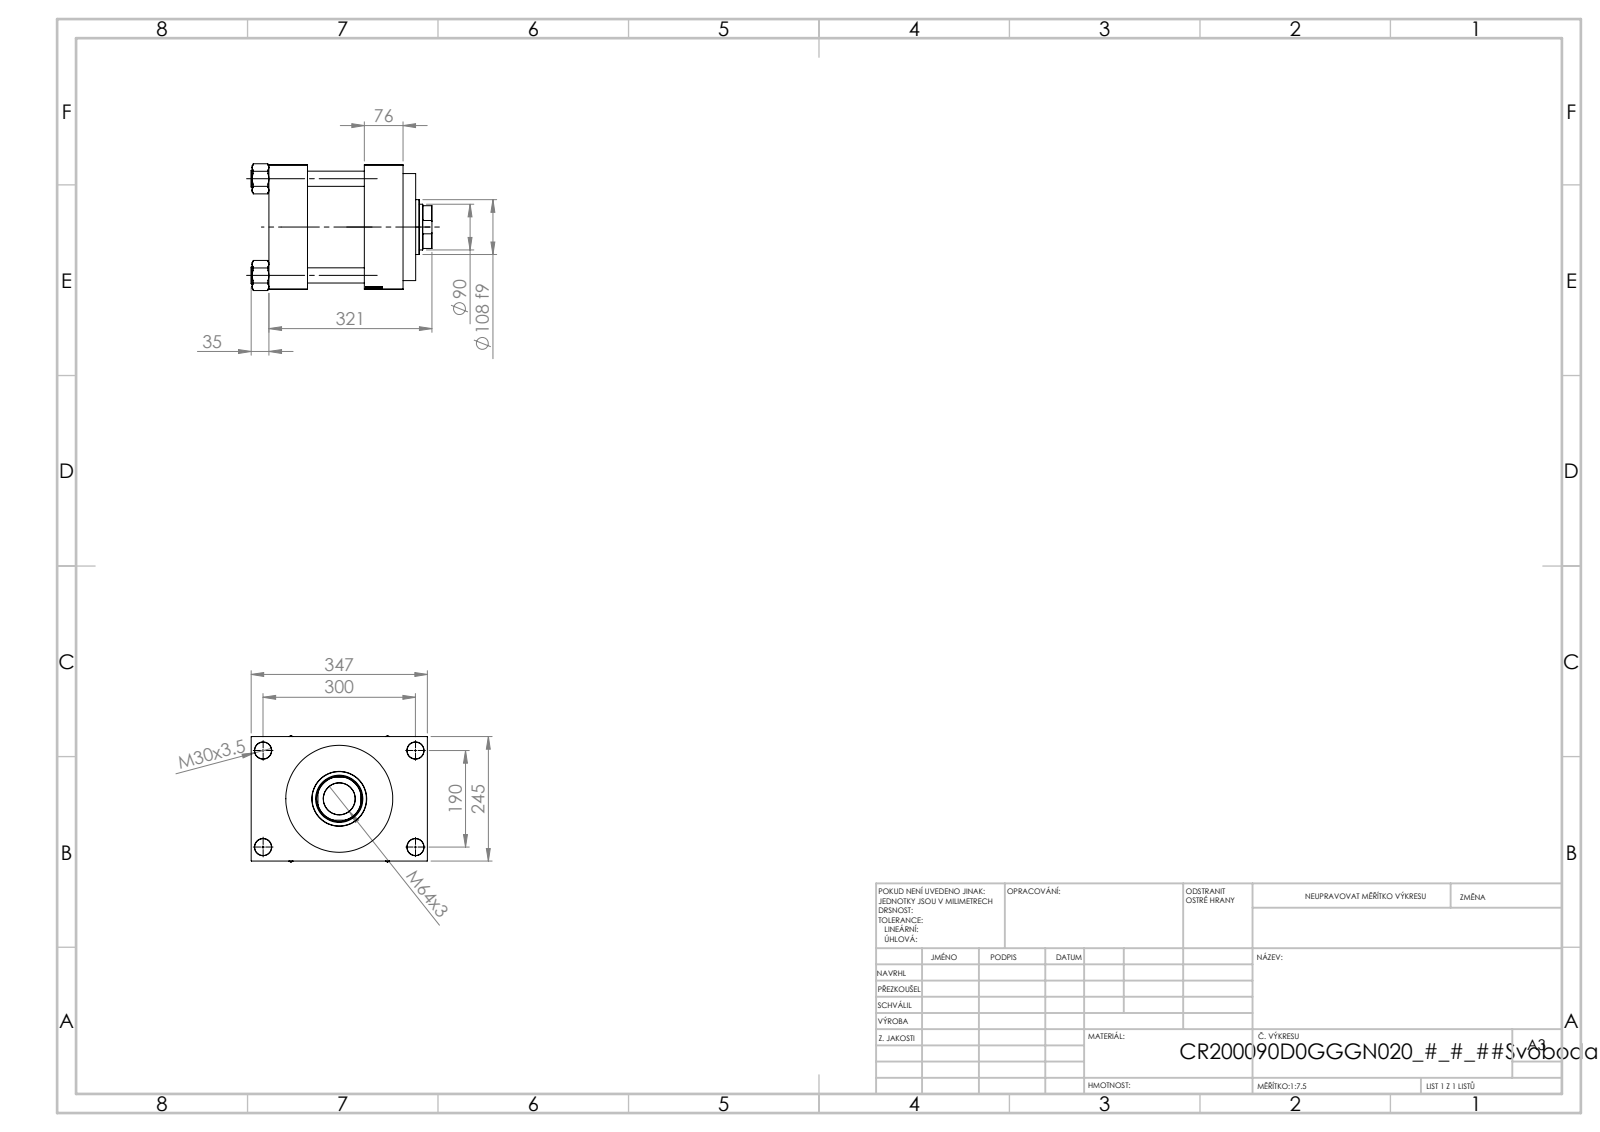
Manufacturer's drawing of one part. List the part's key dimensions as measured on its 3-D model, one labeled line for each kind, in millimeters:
Part name (STEP PRODUCT): V215CR_D_Body; V215_VC_A; V215CR_D_TYCINKA; V215CR_VCP_D (+1 more)
STEP written by: SolidWorks 2019 (CONFIG_CONTROL_DESIGN)
Units: millimetres
Bodies: 11 solids, 1149 faces (544 planar, 87 cylindrical, 518 other)
Overall size (bounding box): 356 × 347 × 249.44
Volume: 14 720 000 mm³ · Surface area: 1 091 000 mm²
Round holes (diameter × count): ⌀30 ×4, ⌀33 ×4, ⌀7 ×2, ⌀41.92 ×2, ⌀52 ×2, ⌀62.5 ×1, ⌀90 ×1, ⌀93 ×1, ⌀146 ×1, ⌀200 ×1, ⌀210.5 ×1
Round bosses / shafts (diameter × count): ⌀33 ×4, ⌀206 ×1, ⌀108 ×1
Partial cylindrical surfaces — rounded edges, fillets, slot ends (radius × count): R44 ×1
Main face-to-face distances: 76, 188, 245, 112, 264, 245.74, 169.74, 57.74, 18.26, 296
Hole centre spacings: 54.9, 134.49, 177.55, 190.2, 197.87, 245.1, 310.18, 190
